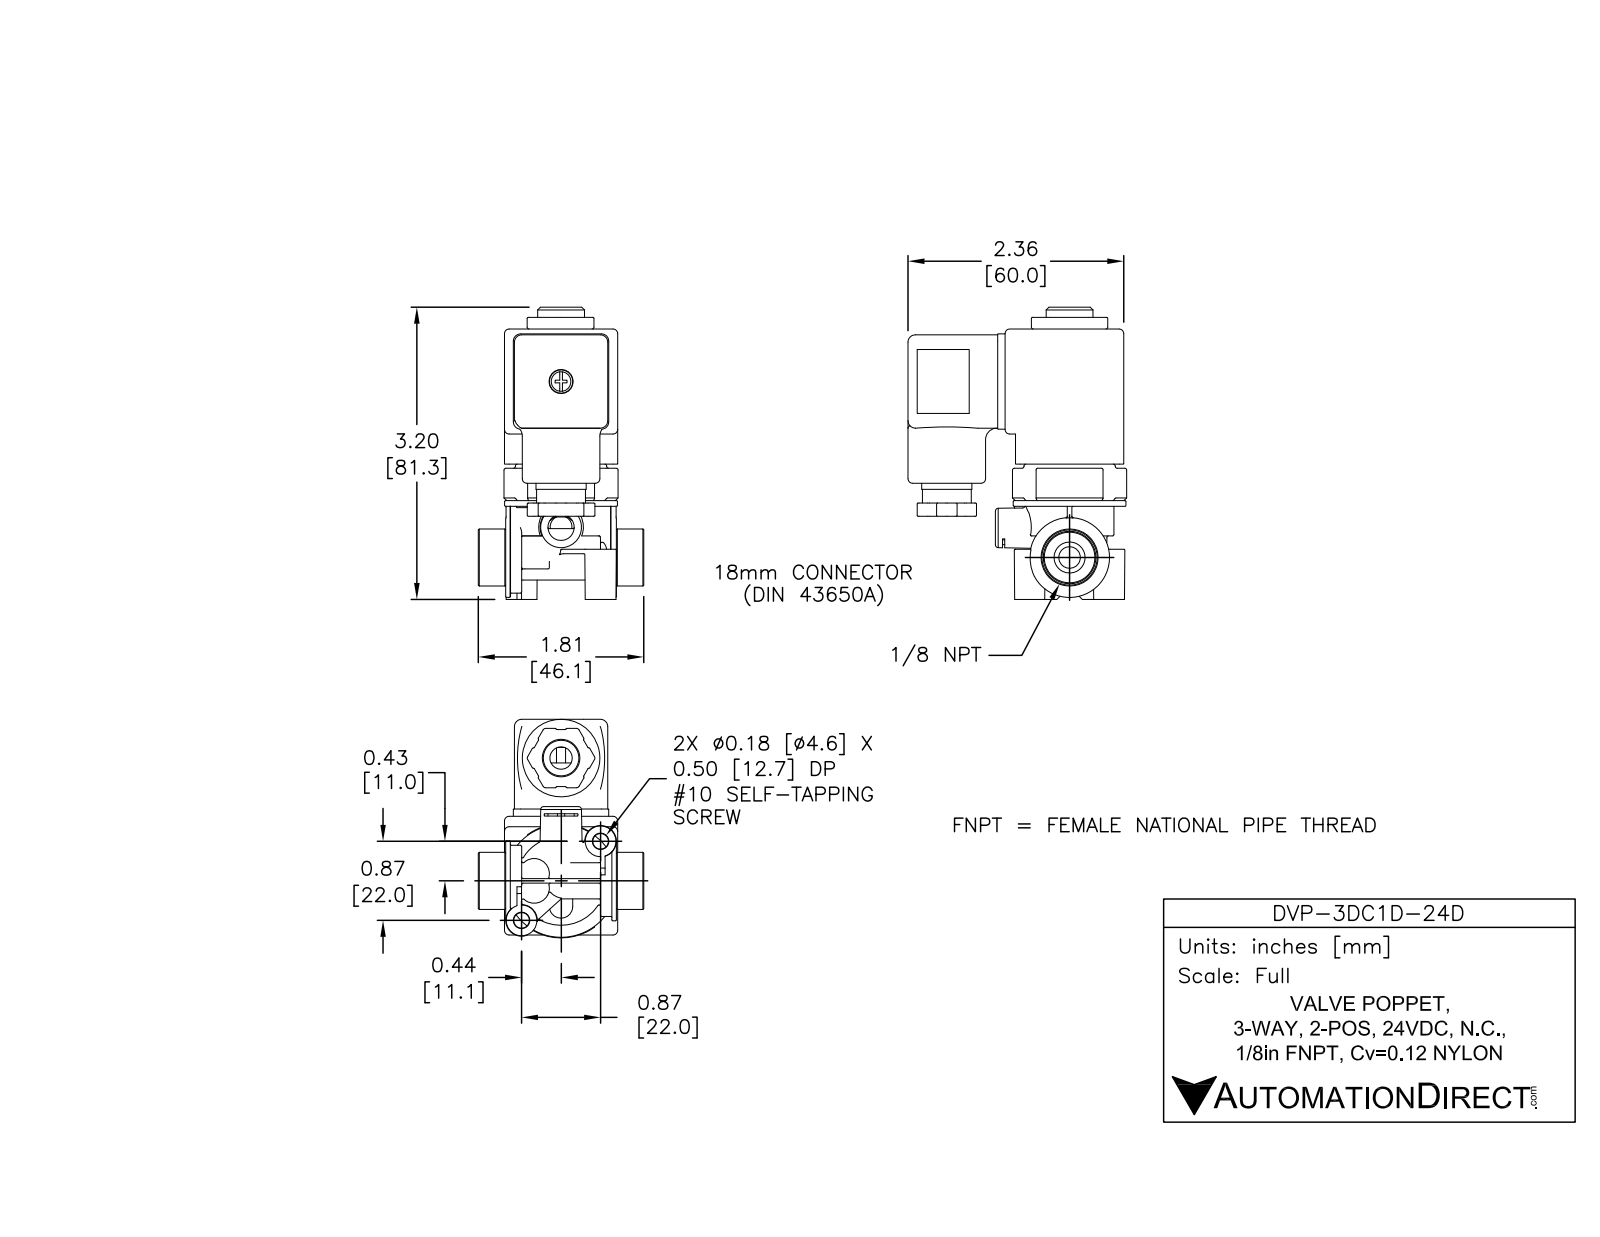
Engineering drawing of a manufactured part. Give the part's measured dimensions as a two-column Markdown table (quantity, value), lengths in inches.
| quantity | value |
| --- | --- |
| part name | DVP-3DC1D-24D |
| STEP written by | SolidWorks 2015 (AUTOMOTIVE_DESIGN) |
| units | inches |
| bodies | 10 solids, 2067 faces (823 planar, 396 cylindrical, 848 other) |
| overall size | 3.204 × 2.395 × 1.813 |
| volume | 4.004 in³ |
| surface area | 57.76 in² |
| round holes (diameter × count) | 0.06 × 2, 0.236 × 2, 0.339 × 2, 0.08 × 1, 0.093 × 1, 0.102 × 1, 0.12 × 1, 0.137 × 1, 0.203 × 1, 0.245 × 1, 0.263 × 1, 0.287 × 1 |
| round bosses / shafts (diameter × count) | 0.29 × 2, 1.236 × 1, 1 × 1, 0.972 × 1, 0.922 × 1, 0.89 × 1, 0.875 × 1, 0.85 × 1 |
| partial cylindrical surfaces (radius × count) | 0.01 × 85, 0.015 × 50, 0.05 × 21, 0.02 × 12, 0.08 × 12, 0.026 × 6, 0.03 × 6, 0.04 × 4 |
| main face-to-face distances | 1.083, 1.24, 0.048, 0.157, 0.925, 1.48, 0.109, 1.131, 0.974, 1.367 |
| hole center spacings | 0.281, 0.283, 1.062, 1.343, 1.345, 1.612, 1.626, 2.184 |
